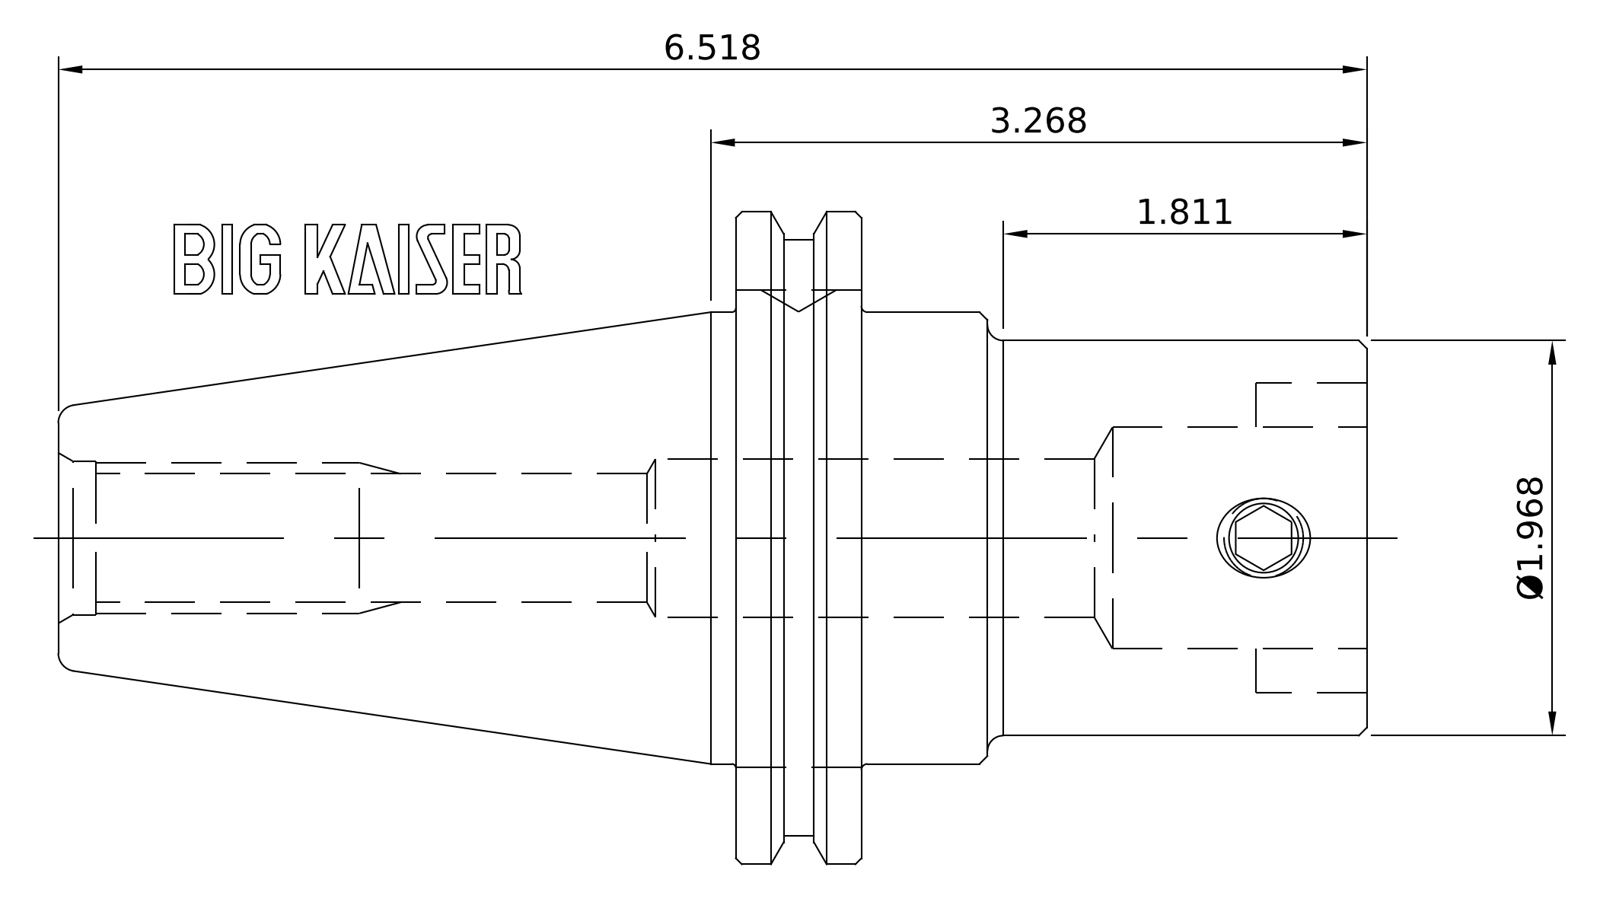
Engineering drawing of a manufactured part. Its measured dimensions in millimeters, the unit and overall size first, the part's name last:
Units: millimetres
Overall size (bounding box): 165.55 × 82.55 × 82.55
Round bosses / shafts (diameter × count): ⌀82.55 ×1, ⌀75.41 ×1, ⌀57.15 ×1, ⌀50 ×1
Main face-to-face distances: 15.88, 63.95, 79.83, 165.55, 101.6, 85.72, 48, 15.95, 31.83, 117.55
Volume: 358 948 mm³ · Surface area: 36 849 mm²
Bodies: 1 solid, 17 faces (7 planar, 6 cylindrical, 4 other)
Part name (STEP PRODUCT): 11.326.552
STEP written by: SolidWorks 2021 (CONFIG_CONTROL_DESIGN)
